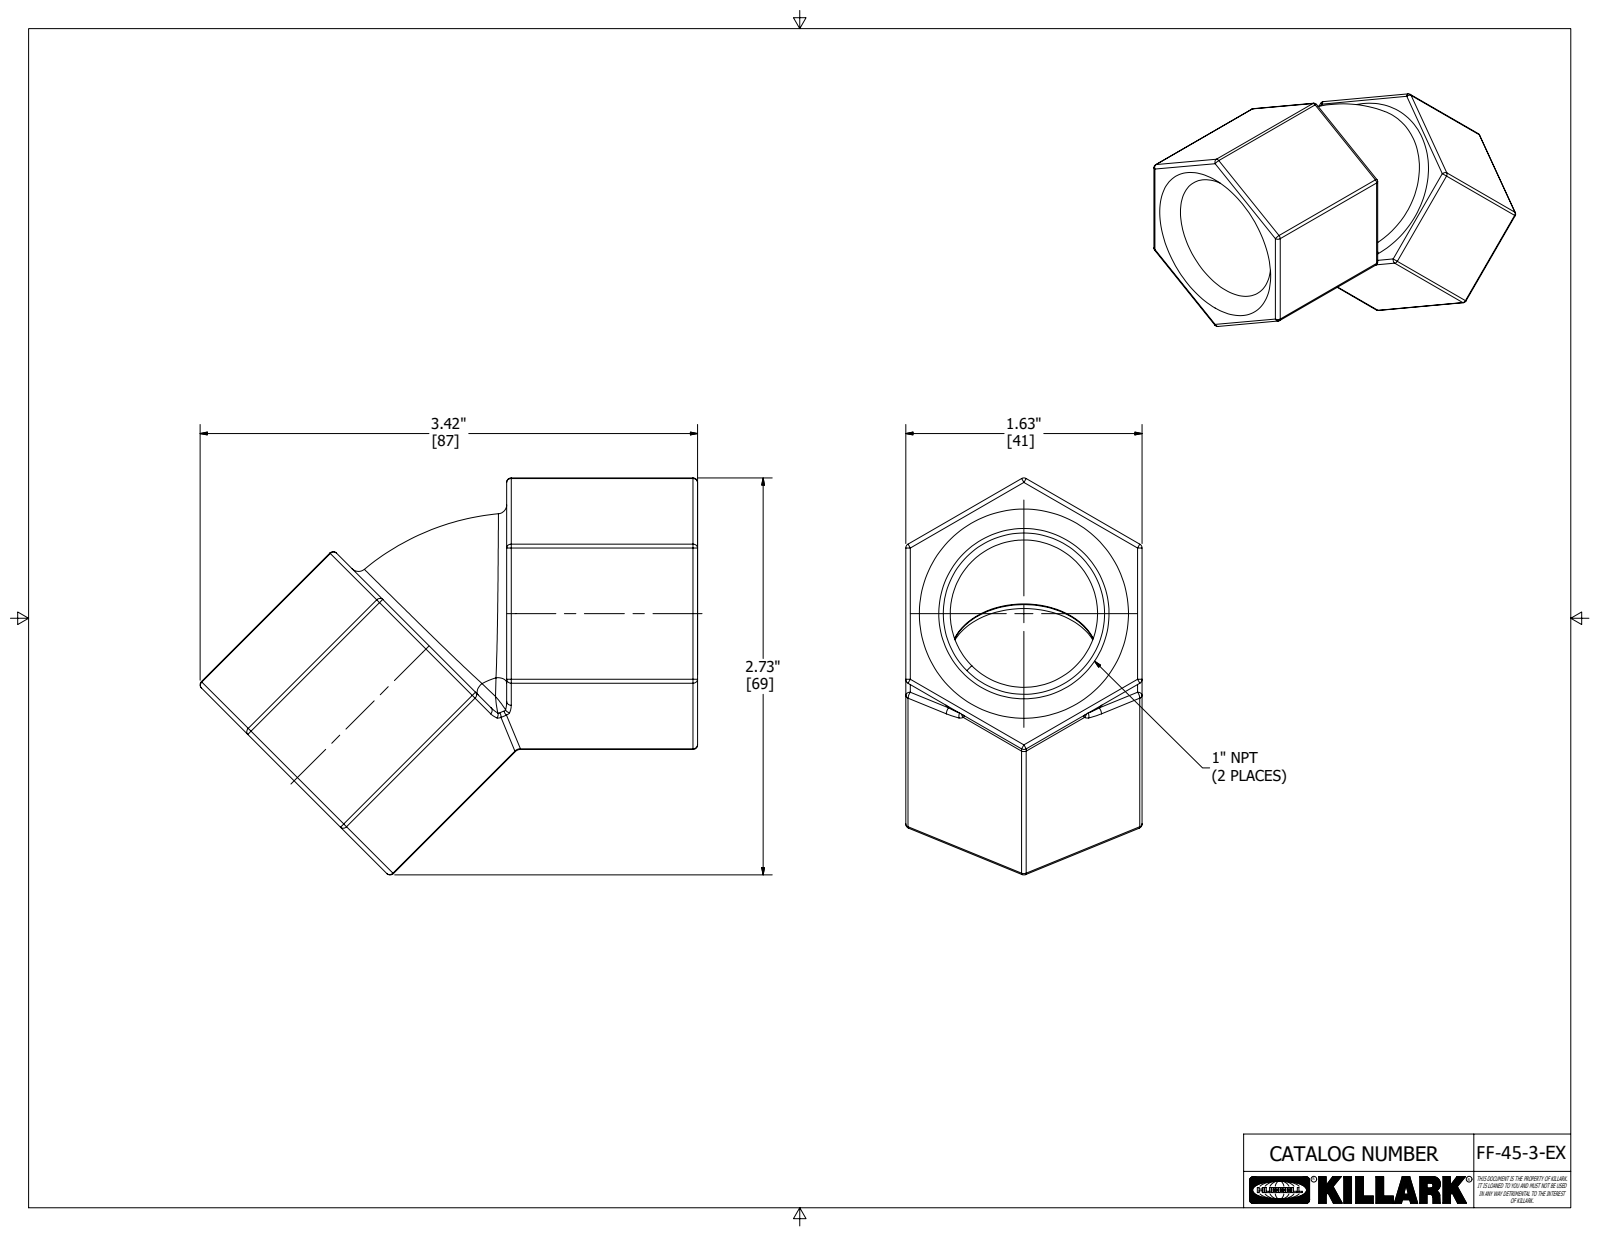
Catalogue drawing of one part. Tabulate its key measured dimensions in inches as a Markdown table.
| quantity | value |
| --- | --- |
| part name | FF-45-3 |
| STEP written by | Autodesk Inventor 2020 (AUTOMOTIVE_DESIGN) |
| units | inches |
| bodies | 1 solid, 109 faces (16 planar, 38 cylindrical, 55 other) |
| overall size | 3.421 × 2.729 × 1.625 |
| volume | 3.723 in³ |
| surface area | 31.1 in² |
| partial cylindrical surfaces (radius × count) | 0.031 × 36, 0.062 × 2 |
| main face-to-face distances | 1.625, 1.624, 1.624, 1.312 |
